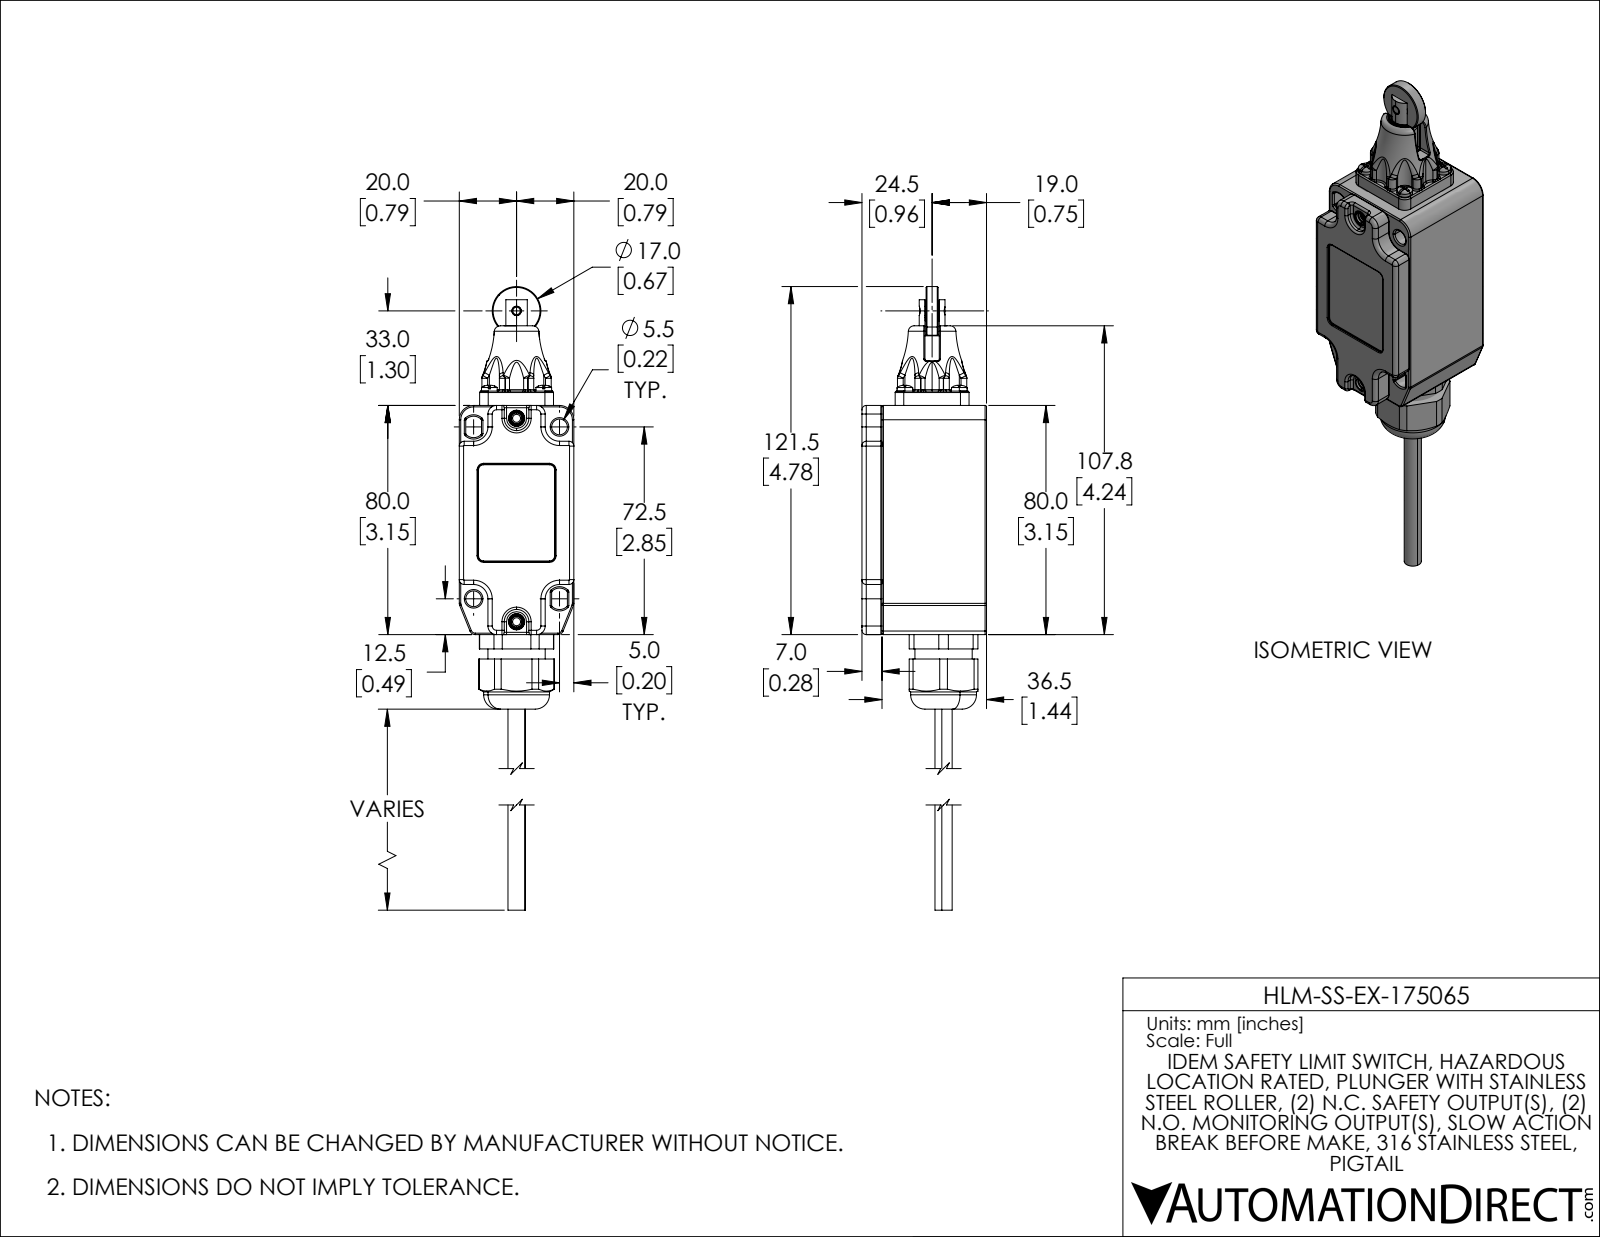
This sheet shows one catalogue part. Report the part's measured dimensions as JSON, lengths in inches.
{"part_name": "HLM-SS-EX-175065", "step_written_by": "SolidWorks 2021 (AUTOMOTIVE_DESIGN)", "units": "inches", "bodies": {"solids": 18, "faces": 2030, "planar": 516, "cylindrical": 526, "other": 988}, "overall_size": [8.091, 1.732, 1.638], "volume_in3": 4.688, "surface_area_in2": 81.42, "round_holes": [[0.102, 10], [0.13, 5], [0.134, 2], [0.157, 2], [0.169, 2], [0.217, 2], [0.059, 1], [0.098, 1], [0.114, 1], [0.173, 1], [0.209, 1], [0.22, 1]], "round_bosses_or_shafts": [[0.236, 7], [0.216, 4], [0.118, 4], [0.276, 3], [0.051, 2], [0.937, 1], [0.89, 1], [0.787, 1]], "partial_cylinders_radius": [[0.02, 122], [0.079, 28], [0.016, 24], [0.006, 14], [0.039, 13], [0.031, 12], [0.138, 8], [0.008, 6]], "face_to_face_distances": [0.12, 1.518, 1.398, 1.638, 1.732, 0.098, 0.236, 1.634, 1.496, 0.087], "hole_center_spacings": [0.748, 0.529, 0.354, 0.432, 0.65, 0.75, 0.828, 0.854]}
